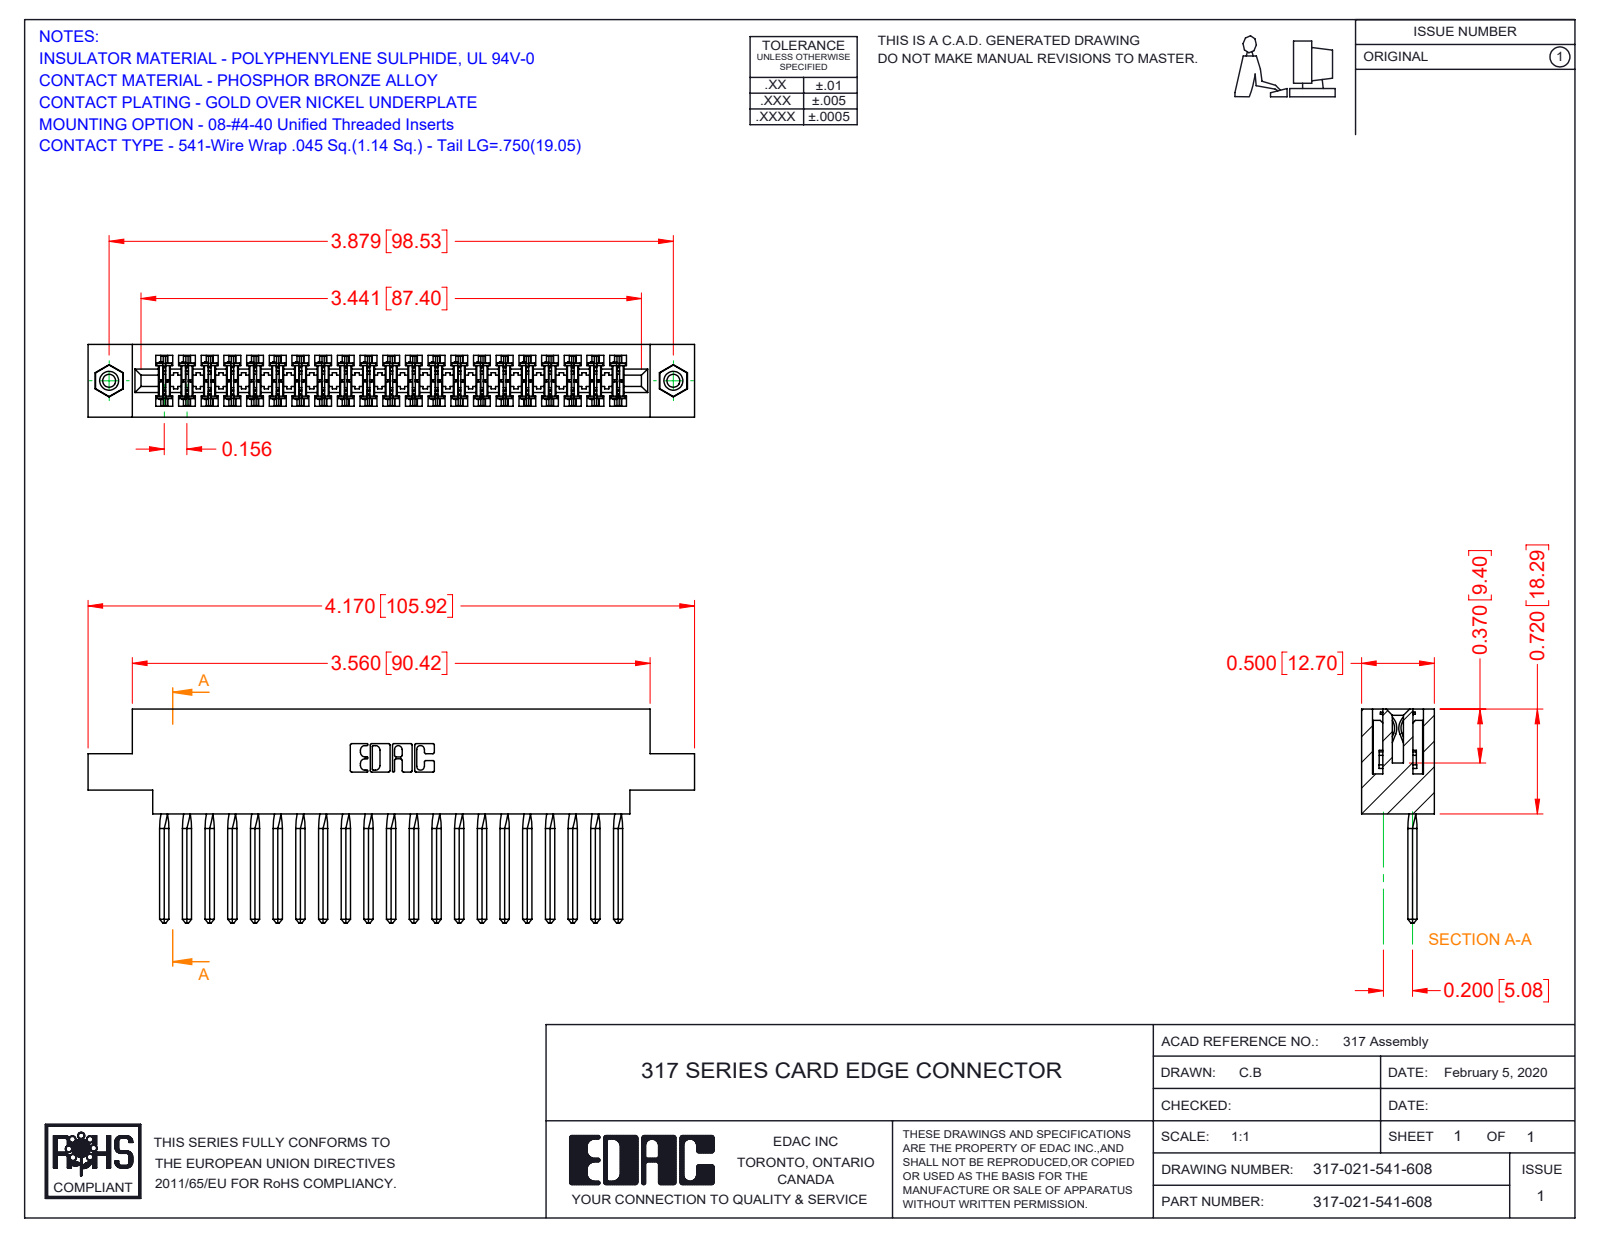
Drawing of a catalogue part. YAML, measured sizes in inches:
part_name: "317-290-002_541; 317 Part_.156 Dia - TI; 345-250-001_345-250-003-102; 317-021-541-678"
step_written_by: "SolidWorks 2016 (CONFIG_CONTROL_DESIGN)"
units: inches
bodies: {solids: 24, faces: 3354, planar: 2694, cylindrical: 560, other: 100}
overall_size: [4.17, 1.47, 0.5]
volume: 1.008
surface_area: 35.14
round_holes:
  - {diameter: 0.089, count: 2}
  - {diameter: 0.125, count: 2}
  - {diameter: 0.156, count: 2}
round_bosses_or_shafts:
  - {diameter: 0.155, count: 2}
partial_cylinders:
  - {radius: 0.015, count: 42}
  - {radius: 0.01, count: 22}
  - {radius: 0.007, count: 6}
  - {radius: 0.031, count: 6}
  - {radius: 0.026, count: 3}
  - {radius: 0.095, count: 2}
  - {radius: 0.1, count: 2}
  - {radius: 0.11, count: 2}
face_to_face_distances: [0.5, 0.075, 0.425, 0.11, 0.35, 0.195, 0.772, 0.22, 0.662, 0.72]
hole_center_spacings: [3.879]
